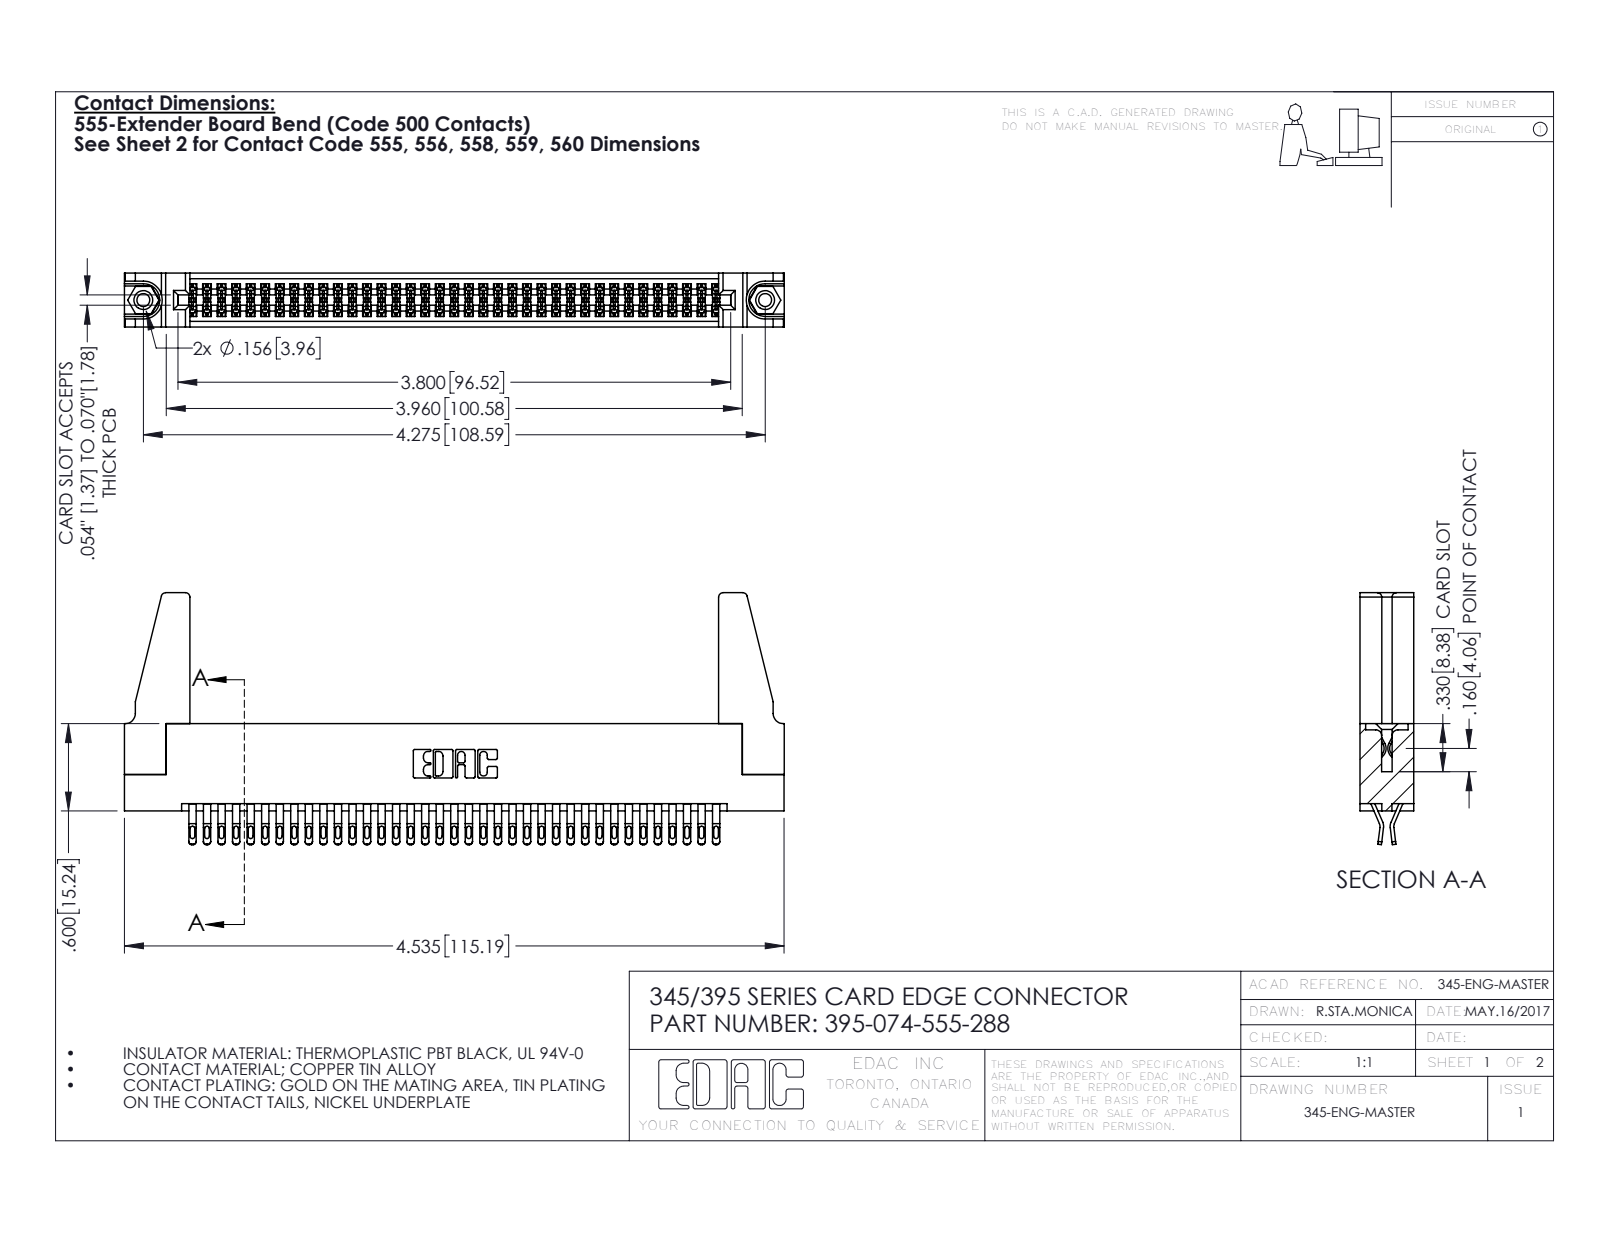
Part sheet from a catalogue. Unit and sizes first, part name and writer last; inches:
Units: inches
Overall size (bounding box): 4.536 × 1.732 × 0.37
Round holes (diameter × count): ⌀0.089 ×2, ⌀0.125 ×2, ⌀0.156 ×2, ⌀0.064 ×1
Round bosses / shafts (diameter × count): ⌀0.155 ×2
Partial cylindrical surfaces — rounded edges, fillets, slot ends (radius × count): R0.016 ×185, R0.02 ×148, R0.006 ×111, R0.01 ×22, R0.03 ×8, R0.007 ×6, R0.031 ×6, R0.026 ×3
Main face-to-face distances: 0.072, 0.298, 0.37, 0.025, 0.2, 0.098, 0.272, 0.225, 0.175, 0.149
Hole centre spacings: 0.27, 4.039, 4.275
Volume: 0.892 in³ · Surface area: 31.87 in²
Bodies: 79 solids, 4394 faces (2446 planar, 1932 cylindrical, 16 other)
Part name (STEP PRODUCT): 345-292-001_555 Tail; 345-250-001_345-250-001-102; 395-074-555-288; 345-220-078_345-220-088 (+1 more)
STEP written by: SolidWorks 2016 (CONFIG_CONTROL_DESIGN)
